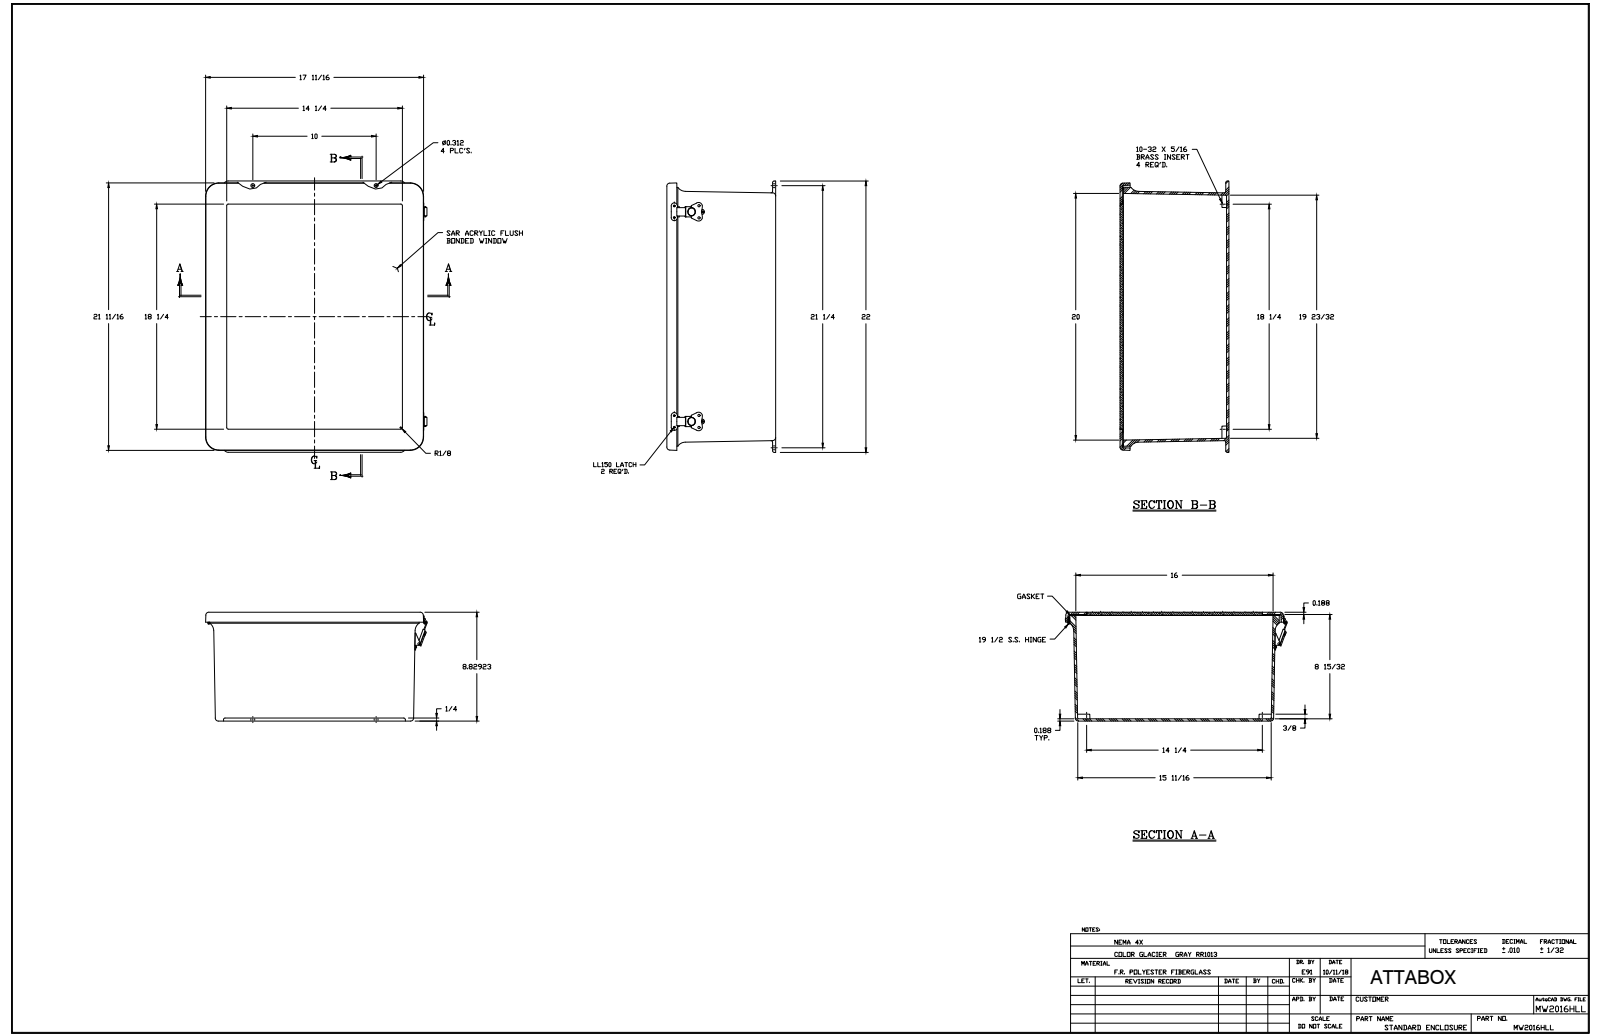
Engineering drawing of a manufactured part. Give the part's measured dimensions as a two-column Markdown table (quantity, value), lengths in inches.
| quantity | value |
| --- | --- |
| part name | MW2016HLL |
| STEP written by | SolidWorks 2018 (AUTOMOTIVE_DESIGN) |
| units | inches |
| bodies | 65 solids, 1452 faces (688 planar, 567 cylindrical, 197 other) |
| overall size | 22 × 17.835 × 8.814 |
| volume | 301.3 in³ |
| surface area | 3 045 in² |
| round holes (diameter × count) | 0.14 × 20, 0.131 × 12, 0.152 × 5, 0.13 × 4, 0.156 × 4, 0.165 × 4, 0.197 × 4, 0.218 × 4, 0.118 × 2, 0.138 × 2, 0.181 × 2, 0.182 × 2 |
| round bosses / shafts (diameter × count) | 0.25 × 20, 0.125 × 13, 0.125 × 7, 0.27 × 4, 0.583 × 2, 0.524 × 2, 0.209 × 2, 0.185 × 2 |
| partial cylindrical surfaces (radius × count) | 0.031 × 20, 0.079 × 19, 0.125 × 14, 0.25 × 12, 0.039 × 8, 0.047 × 8, 0.059 × 5, 0.037 × 4 |
| main face-to-face distances | 0.187, 8.814, 0.188, 8.626, 0.25, 8.564, 8.376, 0.063, 8.627, 8.439 |
| hole center spacings | 3.75, 17, 7.5, 0.25, 3.5, 4, 7.25, 7.75 |
